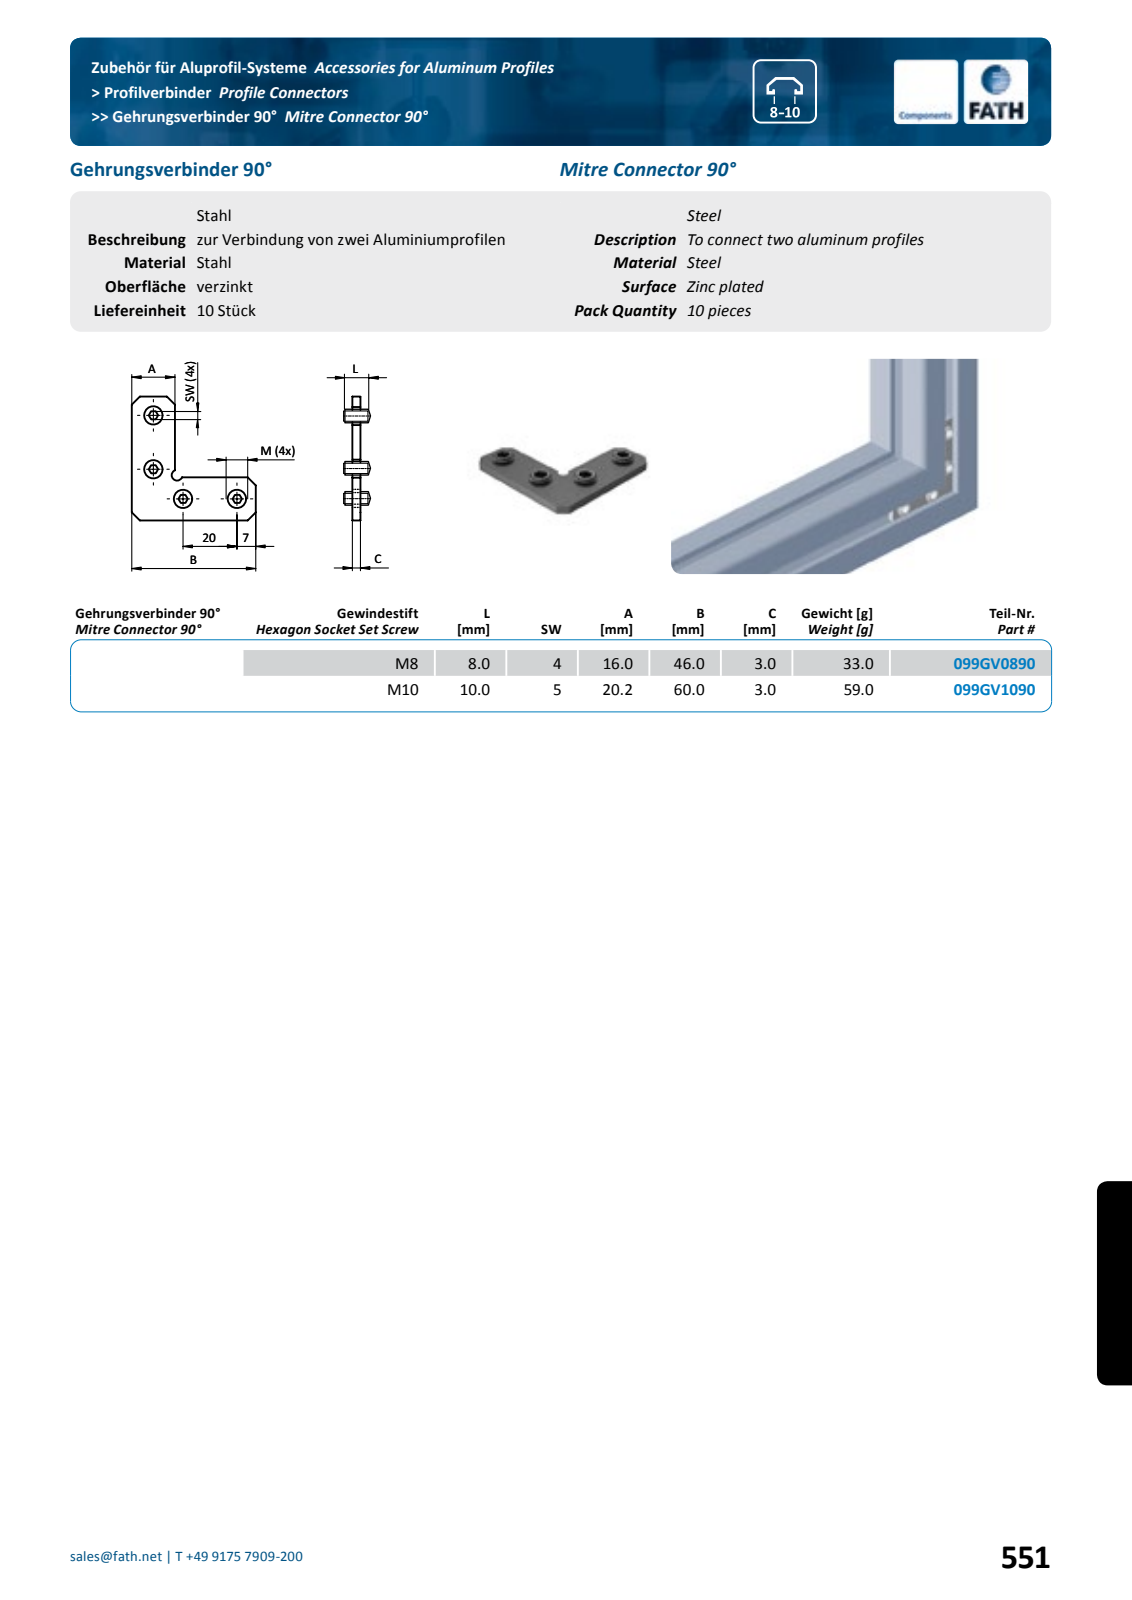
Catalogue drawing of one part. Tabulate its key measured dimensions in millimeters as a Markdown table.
| quantity | value |
| --- | --- |
| part name | fath_099gv0890_1; fath_099gv0890_2; fath_099gv0890_3; fath_099gv0890_4 (+1 more) |
| STEP written by | Spatial InterOp 3D (automotive_design) |
| units | millimeters |
| bodies | 5 solids, 135 faces (93 planar, 18 cylindrical, 24 other) |
| overall size | 46 × 46 × 8 |
| volume | 4 307 mm³ |
| surface area | 4 251 mm² |
| round holes (diameter × count) | 6.8 × 4 |
| round bosses / shafts (diameter × count) | 8 × 4 |
| partial cylindrical surfaces (radius × count) | 2 × 1 |
| main face-to-face distances | 3, 16, 2.5, 5.5, 4, 10, 46, 30, 8, 21 |
| hole center spacings | 20, 32.89, 15.56, 43.84 |
